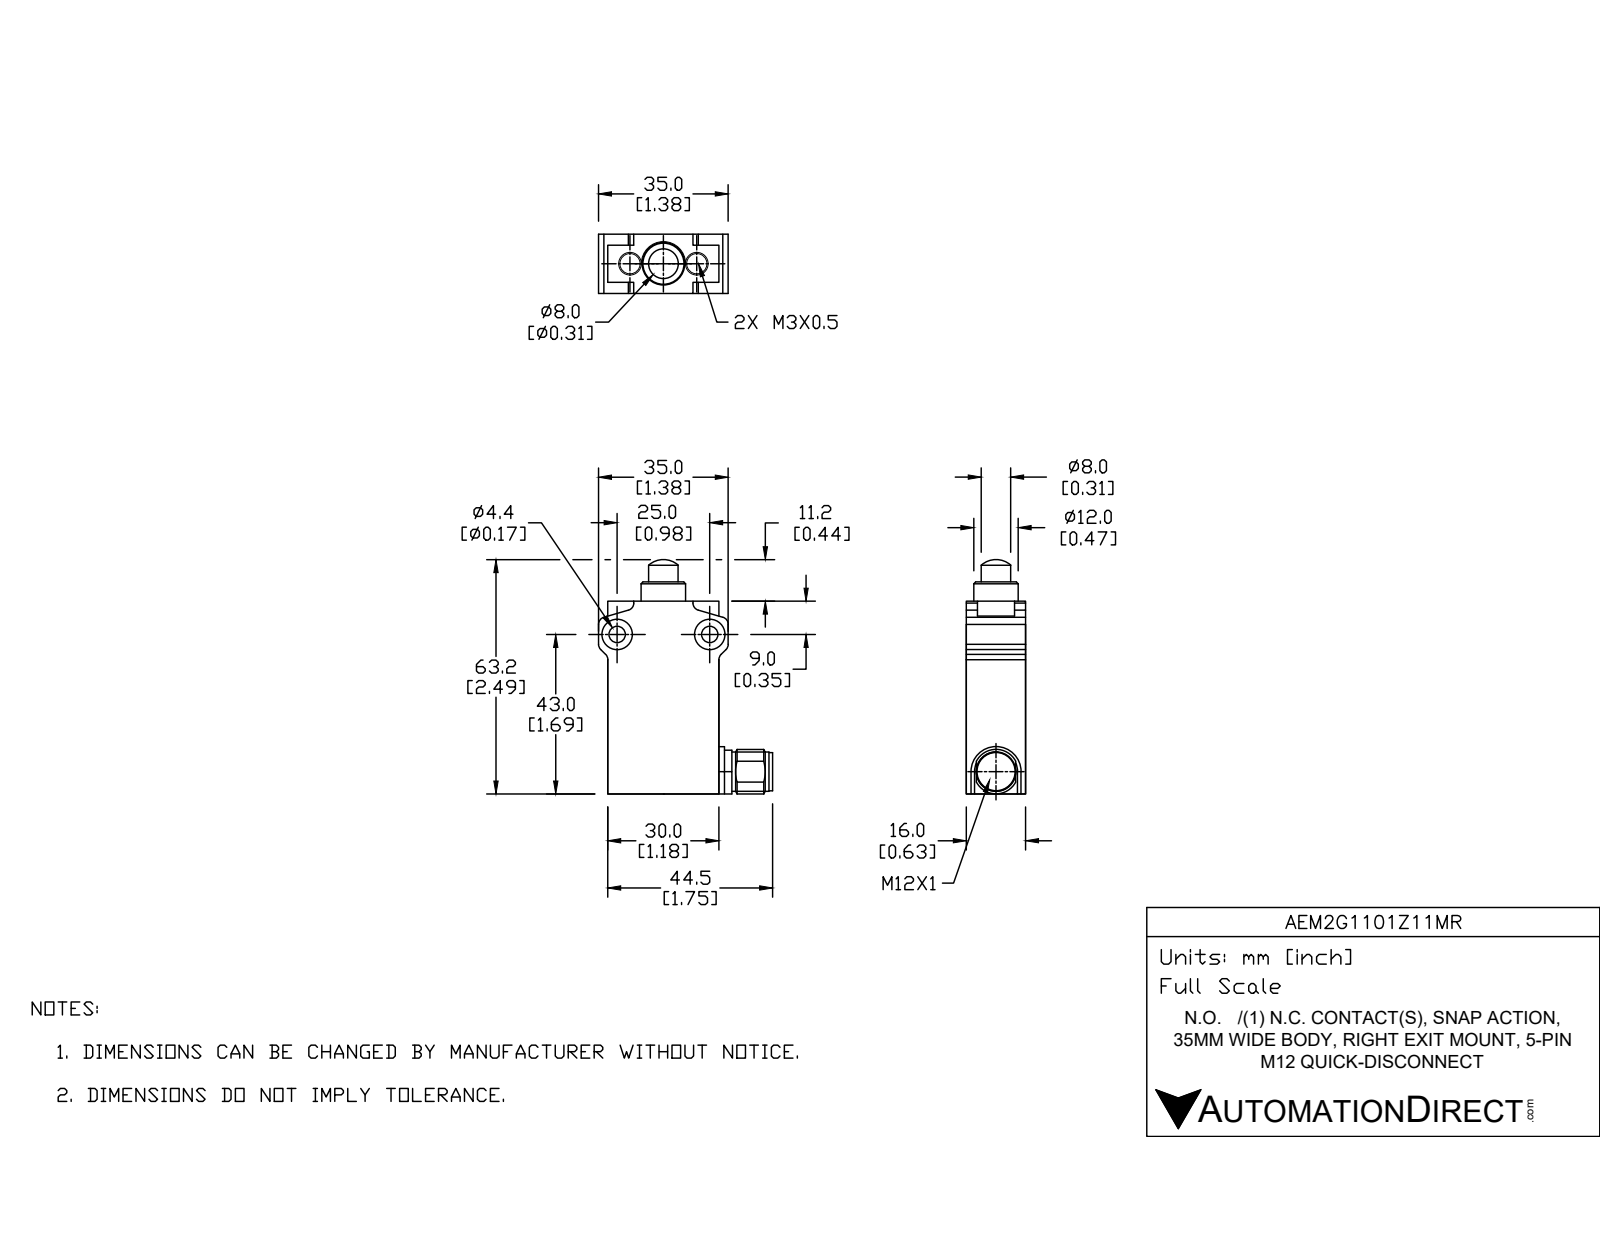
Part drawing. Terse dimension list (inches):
name: AEM2G1101Z11MR
written by: SolidWorks 2019 (AUTOMOTIVE_DESIGN)
unit: in
bodies: 4 solids, 114 faces (42 planar, 43 cylindrical, 29 other)
size: 2.48 × 1.831 × 0.63
volume: 1.569 in³; area: 12.64 in²
holes: 2× ⌀0.118, 2× ⌀0.173, 2× ⌀0.323, 1× ⌀0.315
bosses: 2× ⌀0.472, 1× ⌀0.417, 1× ⌀0.406
rounds: 8× R0.079, 1× R0.256
face distances: 0.63, 1.181, 2.047, 0.472, 0.098, 1.28, 0.157, 1.858, 0.189, 2.244
hole spacings: 0.374, 0.748, 0.984
